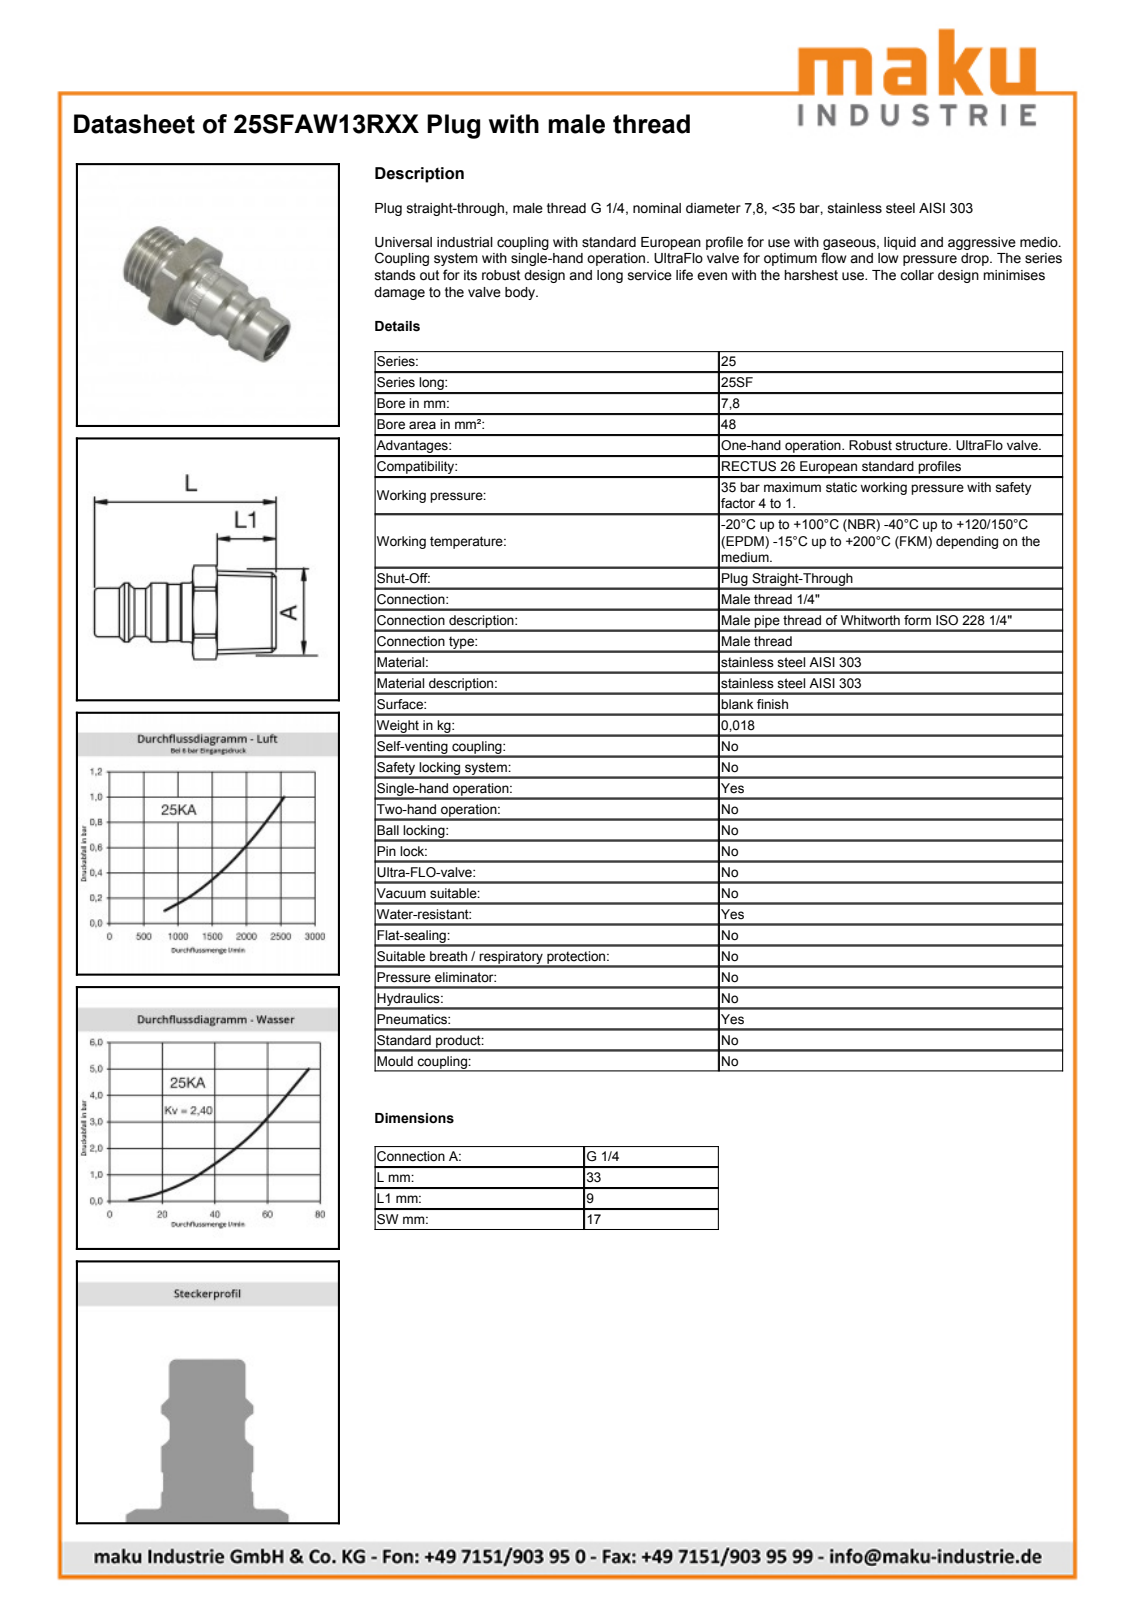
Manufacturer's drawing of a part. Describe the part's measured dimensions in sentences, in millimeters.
The part is named "D110730". Its 3-D file was written by "Autodesk Inventor 2013 (AUTOMOTIVE_DESIGN)". It is 1 solid with 44 faces: 10 planar, 12 cylindrical and 22 other. Overall it measures 33.1 by 19.15 by 17 millimeters. Its volume is 2 453 cubic millimeters and its surface area 2 483 square millimeters. Round holes: 1 of diameter 7.85. Round bosses or shafts: 1 of diameter 13.16, 1 of diameter 12, 1 of diameter 9.9, 1 of diameter 9.75. Partial cylindrical surfaces (rounded edges, fillets, slot ends): 1 of radius 9.57. The main face-to-face distances are 17, 4.1, 13.1, 9, 20, 24.1, 33.1.
